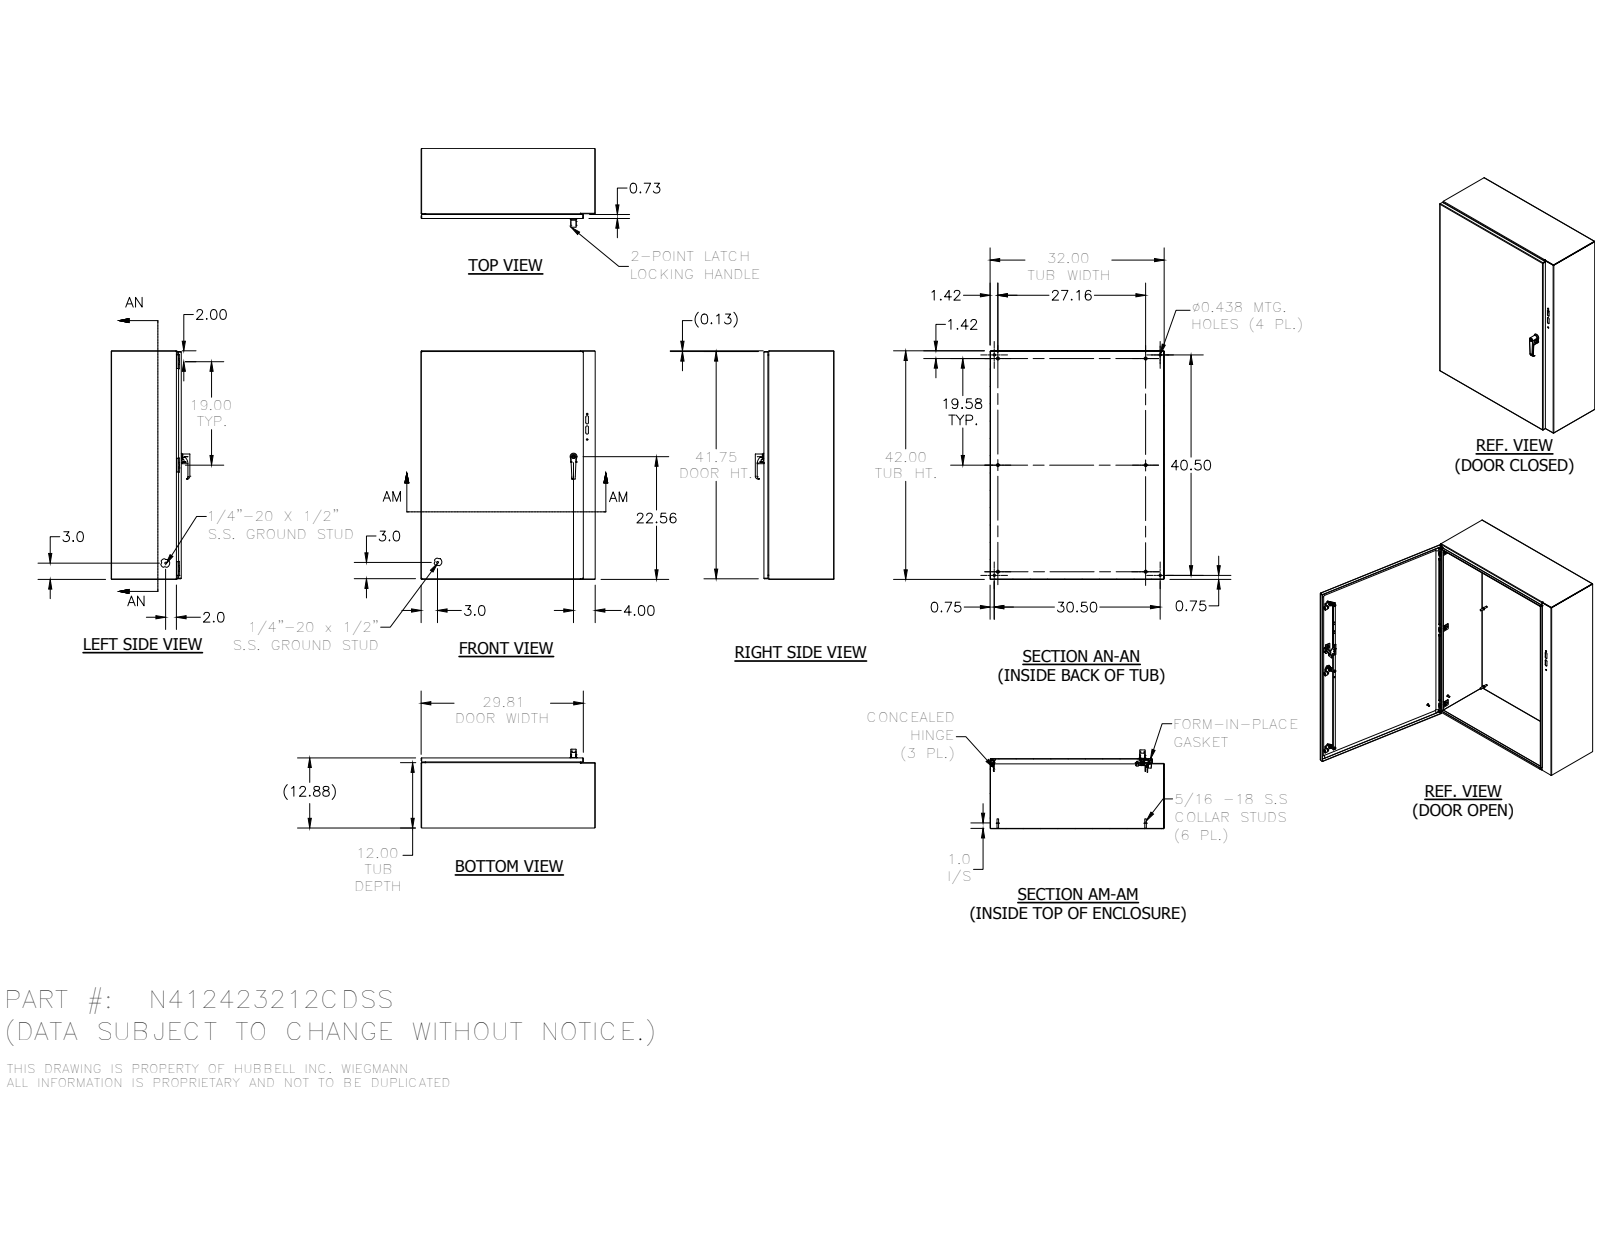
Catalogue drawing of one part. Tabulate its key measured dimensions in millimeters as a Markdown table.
| quantity | value |
| --- | --- |
| part name | N412423212CD |
| STEP written by | SolidWorks 2019 (AUTOMOTIVE_DESIGN) |
| units | millimeters |
| bodies | 81 solids, 2631 faces (1015 planar, 958 cylindrical, 658 other) |
| overall size | 1066.8 × 812.8 × 368.6 |
| volume | 5 894 000 mm³ |
| surface area | 6 230 000 mm² |
| round holes (diameter × count) | 4.8 × 7, 2.4 × 6, 3.7 × 6, 3.9 × 6, 4.2 × 6, 4.4 × 6, 4 × 5, 8.1 × 4, 11.1 × 4, 5 × 3, 5.4 × 3, 5.6 × 3 |
| round bosses / shafts (diameter × count) | 6.4 × 16, 7.6 × 12, 14.3 × 6, 11.1 × 6, 9.1 × 6, 8.1 × 6, 7 × 6, 6.5 × 6 |
| partial cylindrical surfaces (radius × count) | 0.5 × 38, 1.3 × 38, 3.2 × 37, 0.3 × 30, 0.4 × 26, 0.6 × 24, 0.8 × 18, 0.4 × 14 |
| main face-to-face distances | 1.9, 326.2, 324.3, 328.1, 810.9, 1064.9, 809, 812.8, 1063, 1066.8 |
| hole center spacings | 482.6, 426.4, 488, 12.7, 914.4, 965.2, 482.8, 16.7 |
